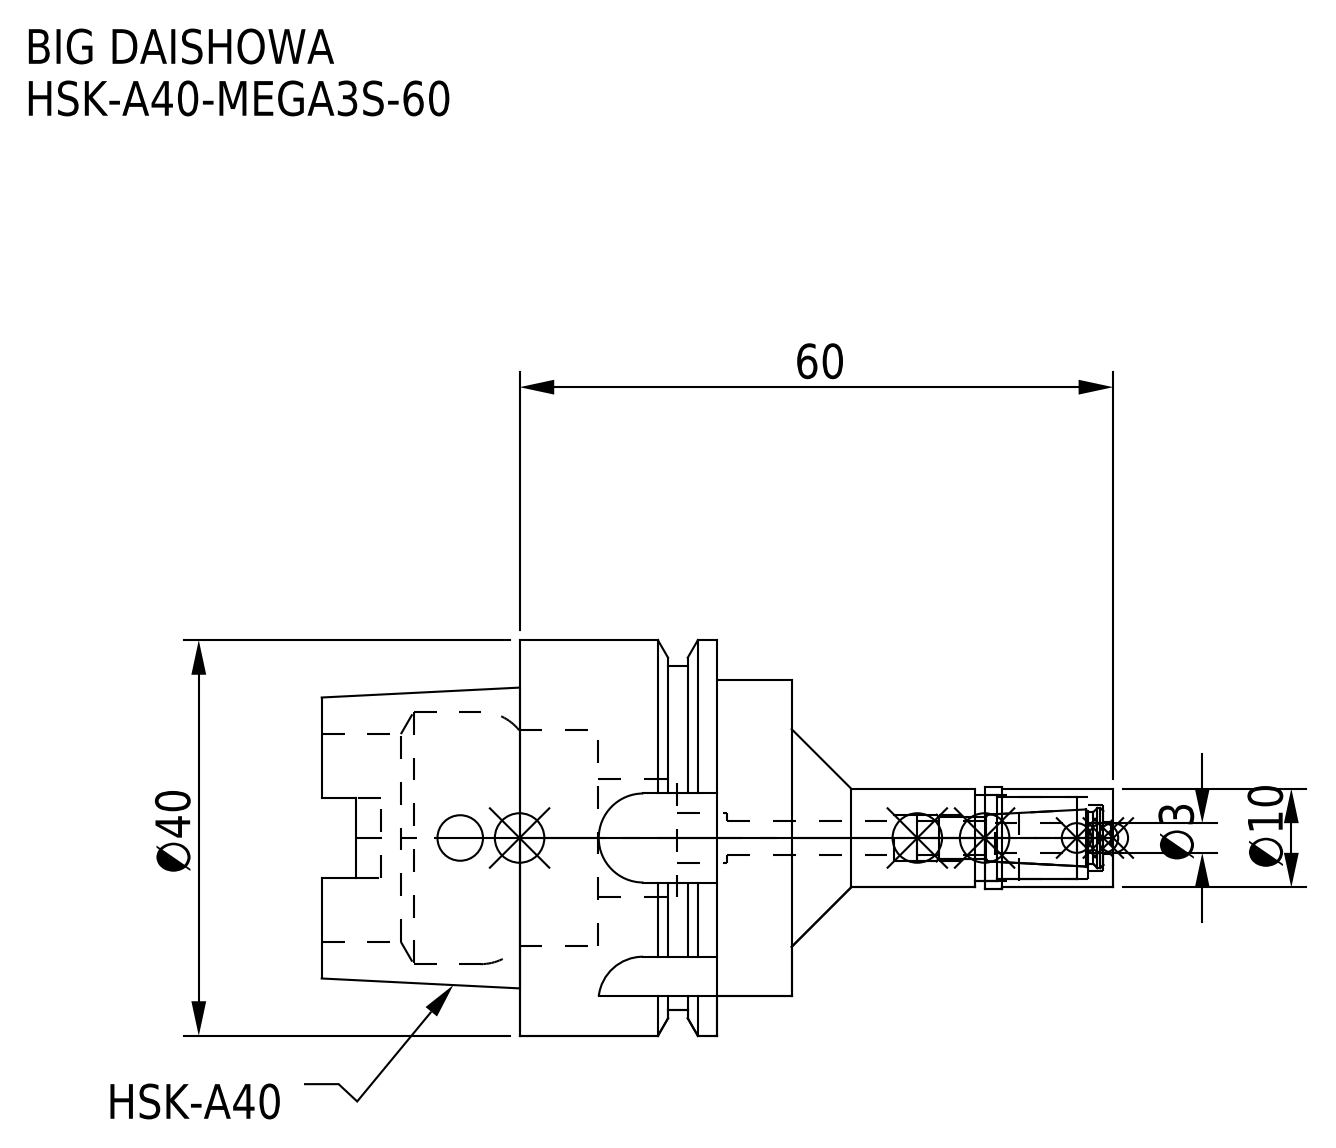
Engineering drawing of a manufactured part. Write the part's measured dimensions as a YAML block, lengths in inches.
part_name: "HSK-A40-MEGA3S-60-030-FreeParts; HA40MS03060-030_ASM.stp; HSK-A40-MEGA3S-60_1.stp; HSK-A40-MEGA3S-60 (+3 more)"
step_written_by: "SolidWorks 2019 (CONFIG_CONTROL_DESIGN)"
units: inches
bodies: {solids: 2, faces: 123, planar: 47, cylindrical: 56, other: 20}
overall_size: [3.15, 1.575, 1.575]
volume: 2.017
surface_area: 19.3
round_holes:
  - {diameter: 0.13, count: 1}
  - {diameter: 0.134, count: 1}
  - {diameter: 0.181, count: 1}
  - {diameter: 0.185, count: 1}
  - {diameter: 0.197, count: 1}
  - {diameter: 0.26, count: 1}
  - {diameter: 0.323, count: 1}
  - {diameter: 0.343, count: 1}
  - {diameter: 0.472, count: 1}
  - {diameter: 0.827, count: 1}
  - {diameter: 0.858, count: 1}
  - {diameter: 1.004, count: 1}
round_bosses_or_shafts:
  - {diameter: 1.575, count: 1}
  - {diameter: 1.37, count: 1}
  - {diameter: 1.26, count: 1}
  - {diameter: 0.406, count: 1}
  - {diameter: 0.394, count: 1}
partial_cylinders:
  - {radius: 0.074, count: 4}
  - {radius: 0.177, count: 4}
face_to_face_distances: [0.787, 1.083, 0.295, 0.77, 0.474, 0.313, 1.575, 1.87, 1.1, 1.339]
